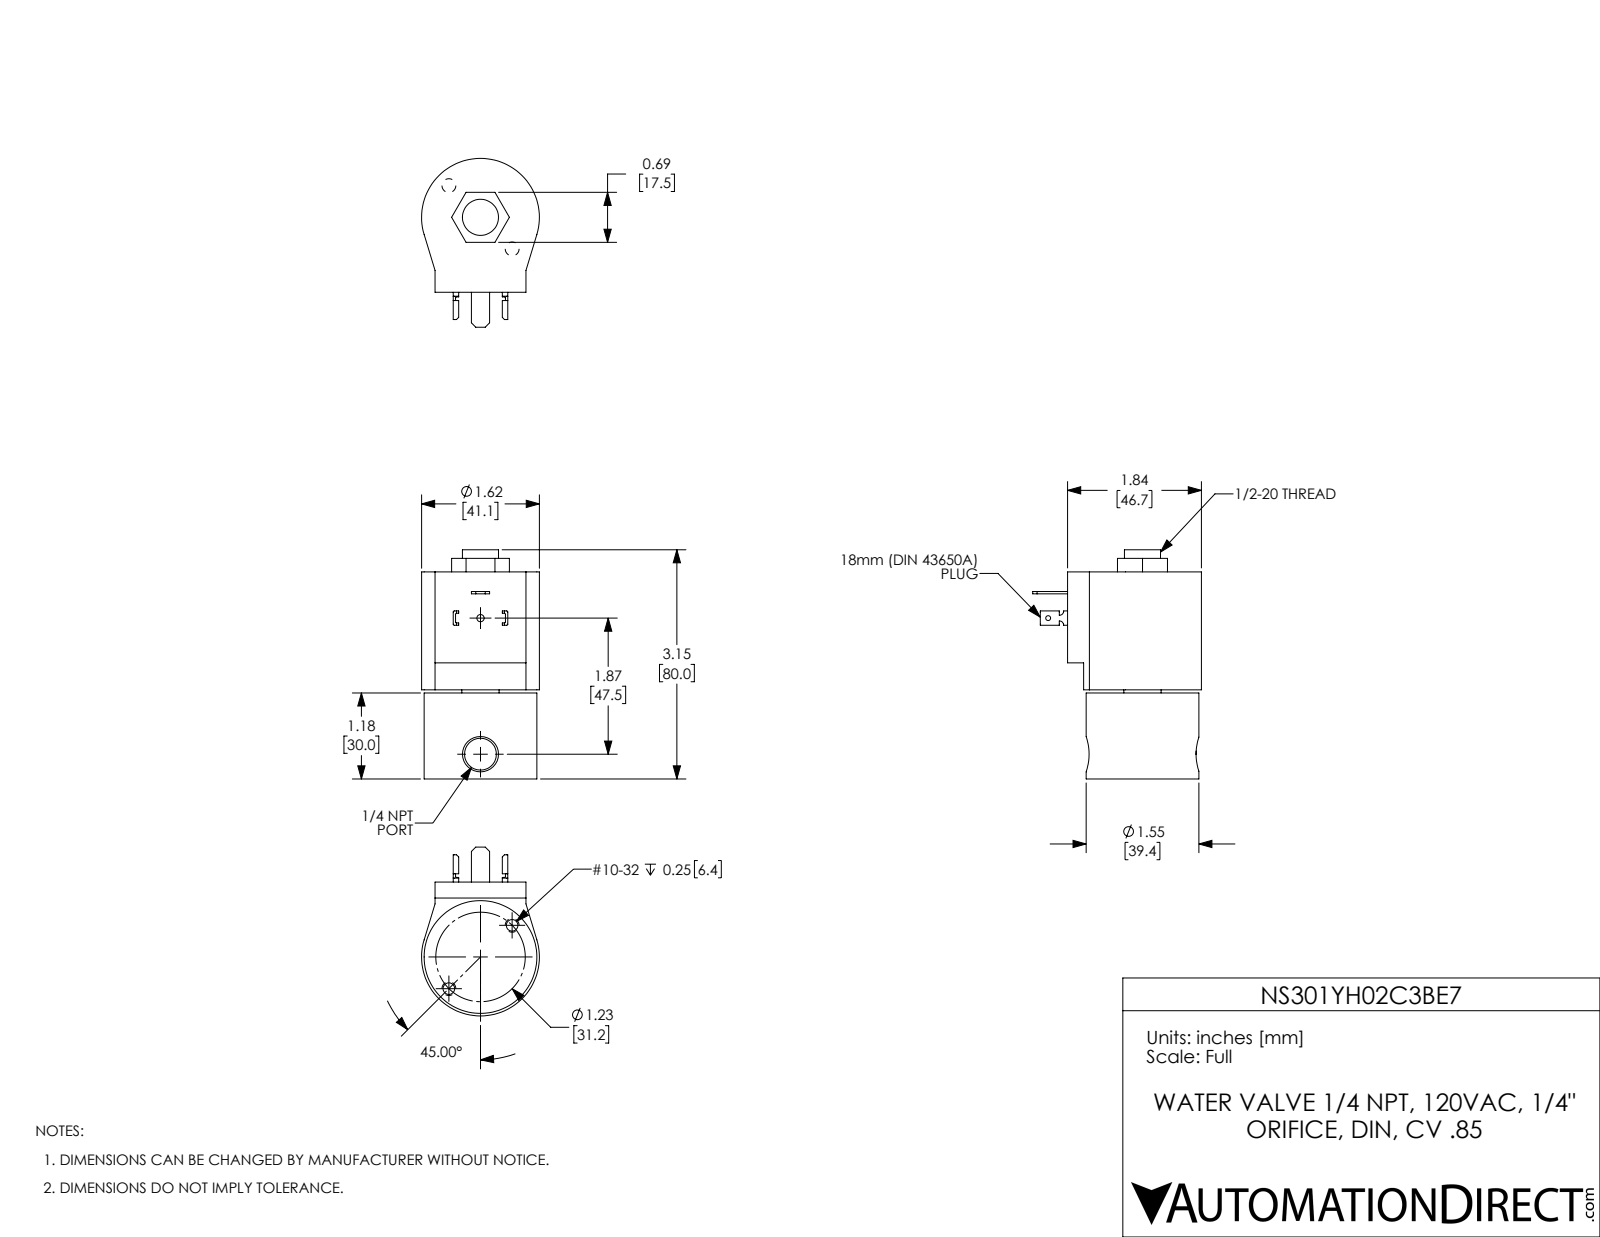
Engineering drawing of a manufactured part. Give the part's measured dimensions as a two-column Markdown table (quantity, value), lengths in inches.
| quantity | value |
| --- | --- |
| part name | NS301YH02C3BE7 |
| STEP written by | SolidWorks 2024 (CONFIG_CONTROL_DESIGN) |
| units | inches |
| bodies | 6 solids, 130 faces (73 planar, 49 cylindrical, 8 other) |
| overall size | 3.15 × 2.32 × 1.62 |
| volume | 6.027 in³ |
| surface area | 33.08 in² |
| round holes (diameter × count) | 0.159 × 2, 0.067 × 1, 0.1 × 1, 0.437 × 1, 0.496 × 1, 0.512 × 1, 1.155 × 1 |
| round bosses / shafts (diameter × count) | 1.55 × 1 |
| partial cylindrical surfaces (radius × count) | 0.015 × 8, 0.06 × 2, 0.81 × 1 |
| main face-to-face distances | 2.845, 1.182, 1.663, 1.225, 0.043, 1.62, 1.287, 0.106, 0.062, 1.558 |
| hole center spacings | 0.615, 1.23, 1.87 |
